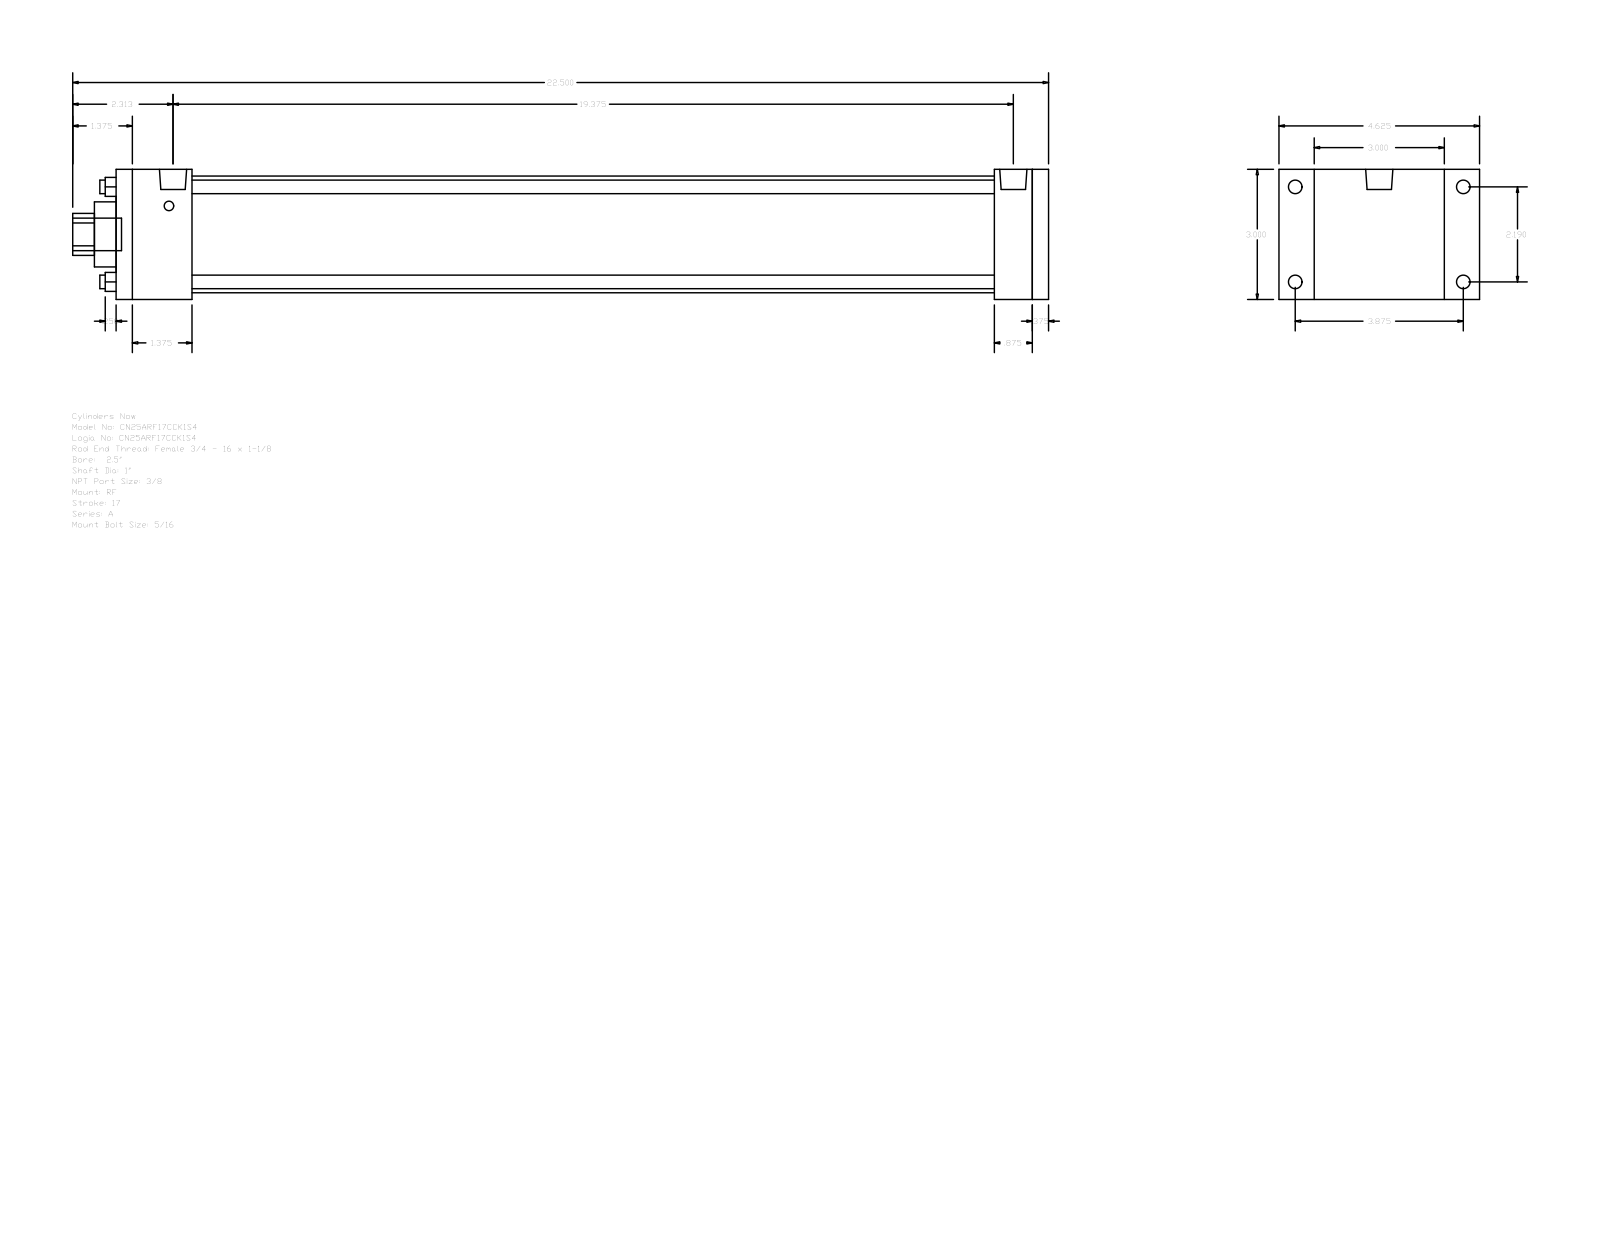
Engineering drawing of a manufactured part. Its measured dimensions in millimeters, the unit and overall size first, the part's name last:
Units: millimetres
Overall size (bounding box): 571.5 × 117.47 × 76.2
Round holes (diameter × count): ⌀7.94 ×4, ⌀25.4 ×1, ⌀38.1 ×1, ⌀68.33 ×1
Round bosses / shafts (diameter × count): ⌀7.94 ×4, ⌀5.56 ×4, ⌀15.93 ×2, ⌀19.05 ×1
Partial cylindrical surfaces — rounded edges, fillets, slot ends (radius × count): R12.29 ×1
Main face-to-face distances: 76.2, 546.1, 9.52, 536.58, 44.45, 514.35, 469.9, 492.13, 501.65, 22.23
Hole centre spacings: 39.33, 55.62, 78.66
Bodies: 0 solids, 92 faces (64 planar, 28 cylindrical, 0 other)
Part name (STEP PRODUCT): A_RF__0250_1
STEP written by: GSSL Pune (CONFIG_CONTROL_DESIGN)
